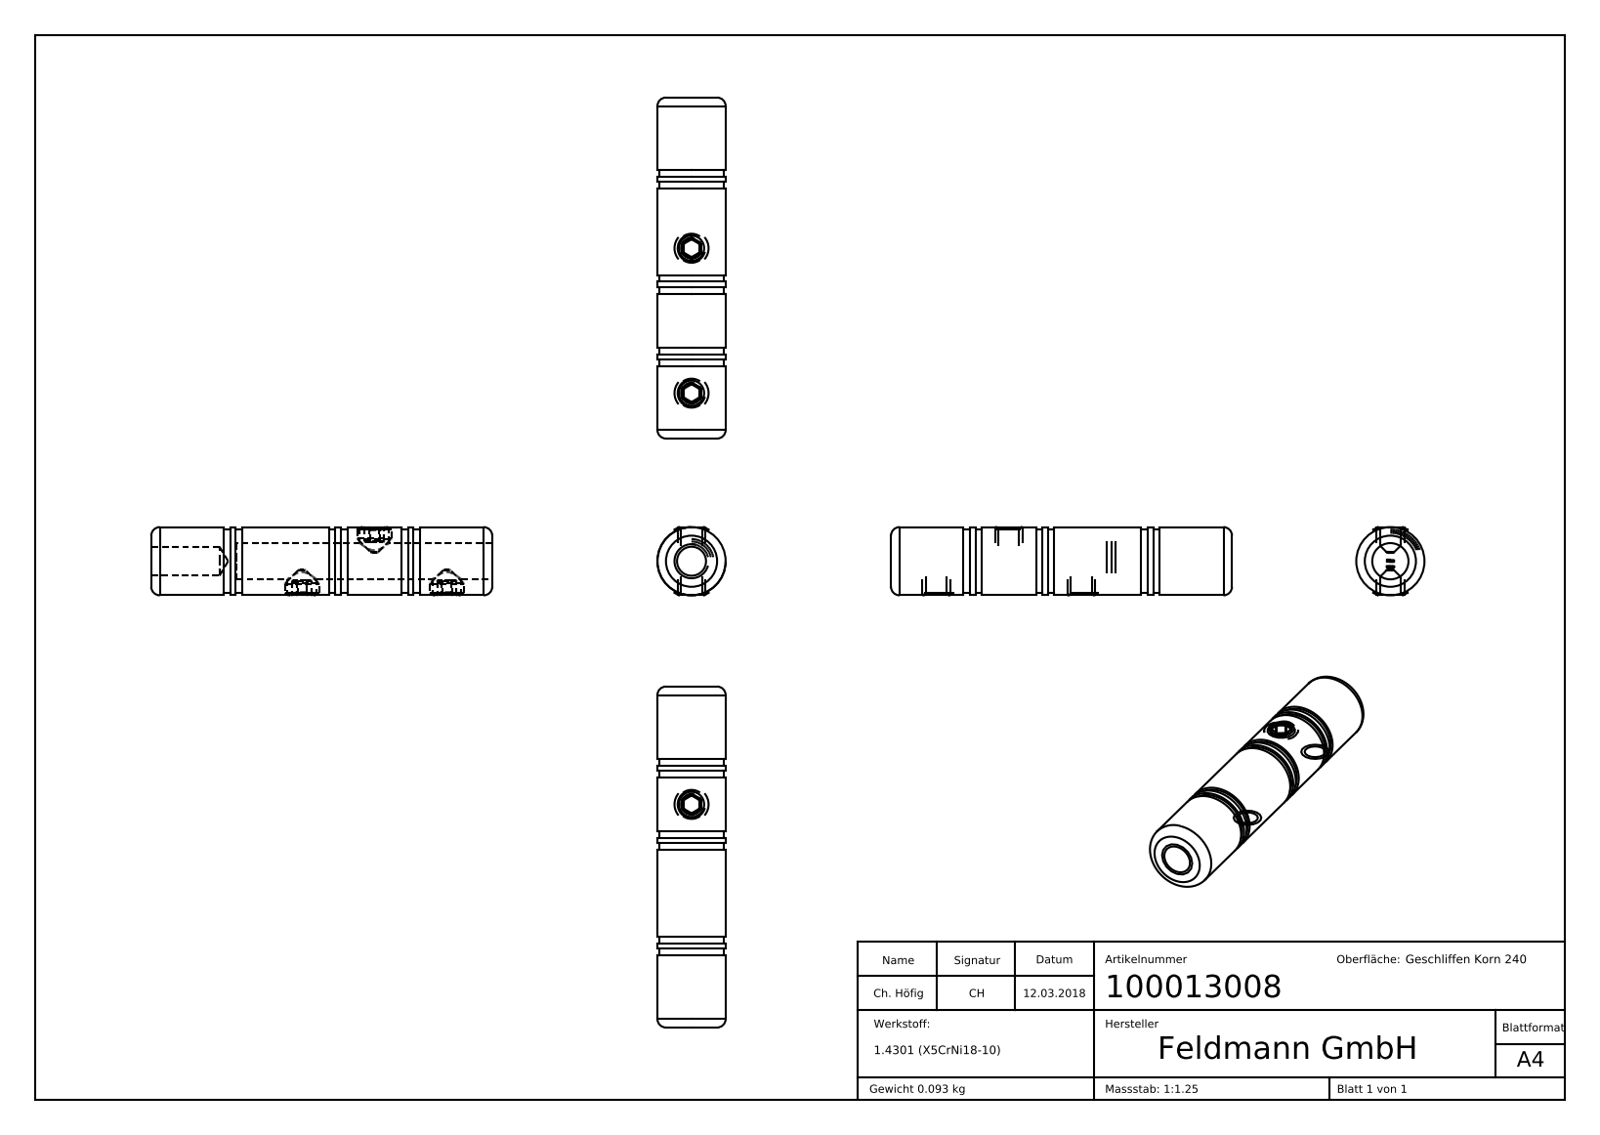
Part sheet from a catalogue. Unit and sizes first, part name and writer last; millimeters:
Units: millimetres
Overall size (bounding box): 80 × 16 × 16
Round holes (diameter × count): ⌀6.8 ×4, ⌀8.5 ×1
Round bosses / shafts (diameter × count): ⌀8 ×3, ⌀16 ×1, ⌀15 ×1
Partial cylindrical surfaces — rounded edges, fillets, slot ends (radius × count): R0.2 ×50
Main face-to-face distances: 1.5, 2.8, 17, 41.7, 1.3, 18.5, 19.8, 24.7, 44.5, 40.2
Hole centre spacings: 17, 34
Volume: 11 792 mm³ · Surface area: 7 254 mm²
Bodies: 4 solids, 424 faces (138 planar, 96 cylindrical, 190 other)
Part name (STEP PRODUCT): 100013008; DIN914_DIN 914 M8x6; 10001X00X Teil 1_100013008 Teil1
STEP written by: SolidWorks 2015 (CONFIG_CONTROL_DESIGN)
